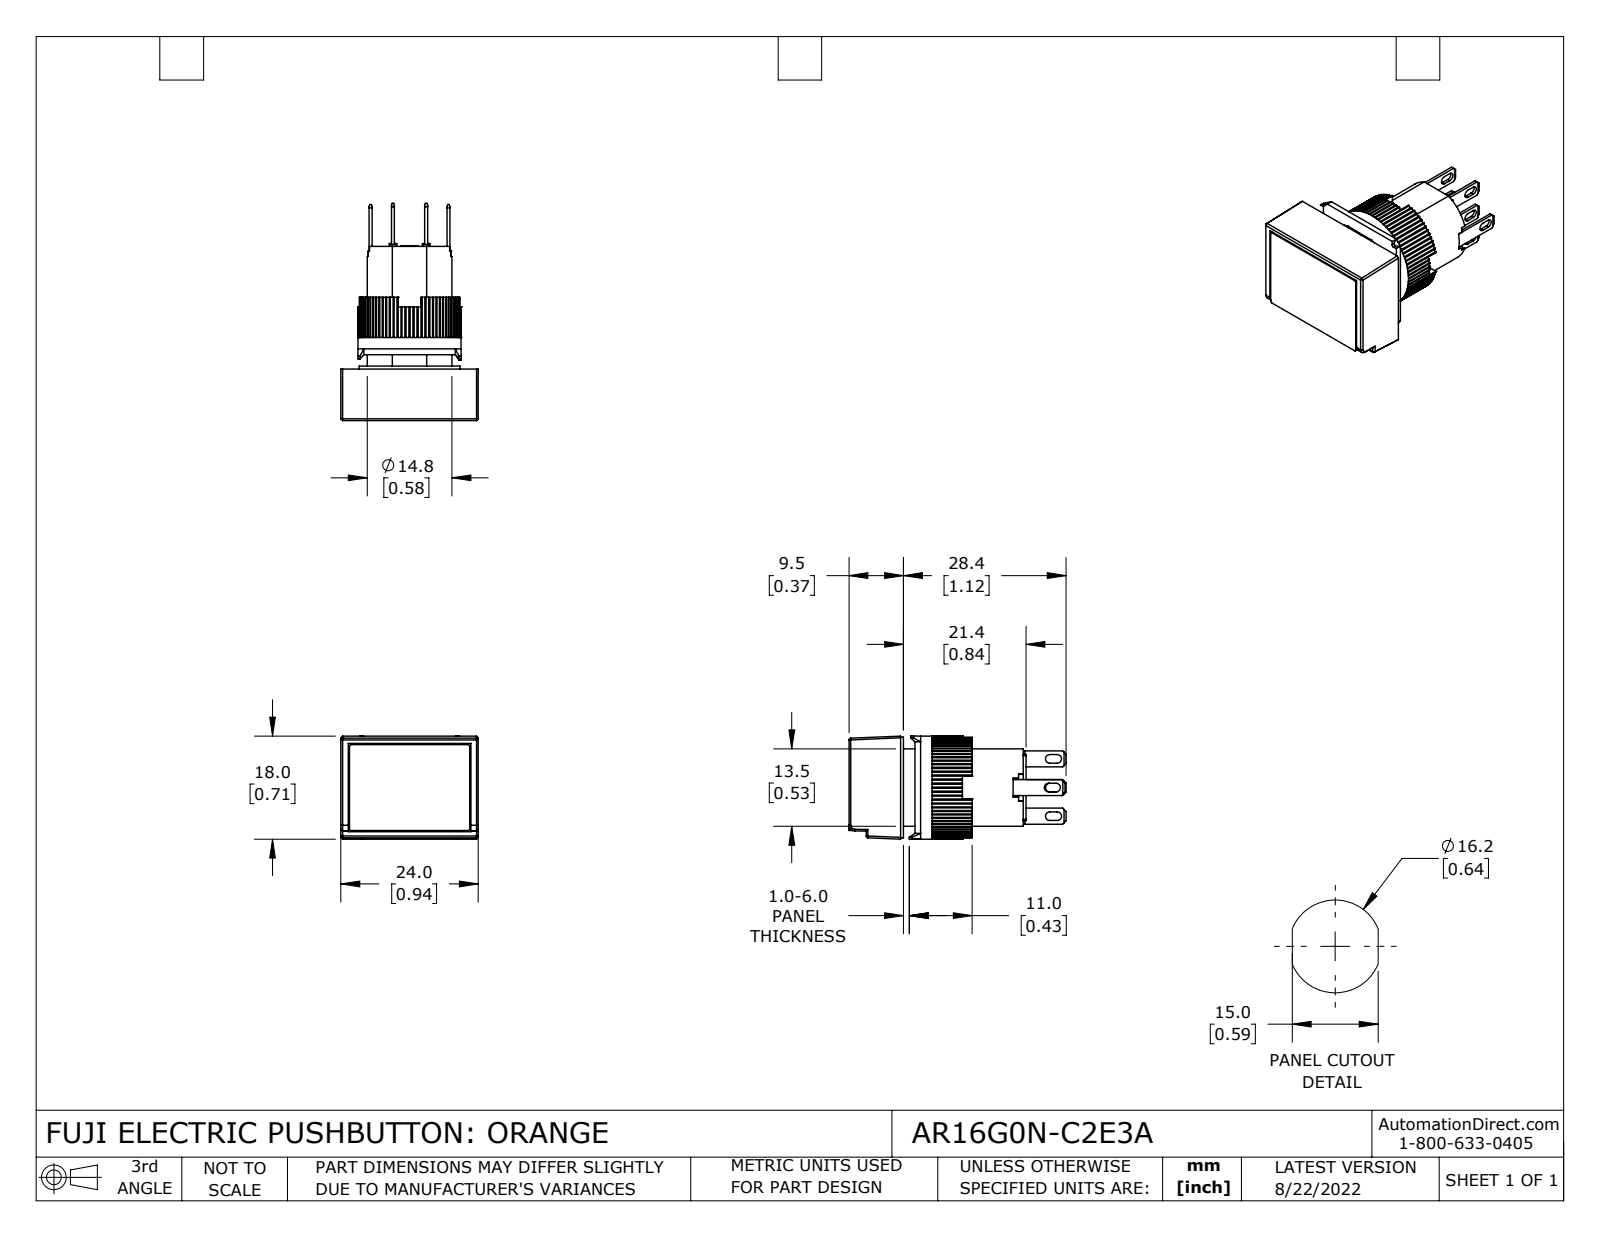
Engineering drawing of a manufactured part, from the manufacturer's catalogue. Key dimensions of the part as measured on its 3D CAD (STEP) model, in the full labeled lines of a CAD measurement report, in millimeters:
Part name (STEP PRODUCT): AR16G0N-C2E3A
STEP written by: SolidWorks 2021 (CONFIG_CONTROL_DESIGN)
Units: millimetres
Bodies: 14 solids, 841 faces (654 planar, 181 cylindrical, 6 other)
Overall size (bounding box): 37.9 × 24 × 18
Volume: 7 340 mm³ · Surface area: 6 131 mm²
Round holes (diameter × count): ⌀13.8 ×1, ⌀14.8 ×1
Round bosses / shafts (diameter × count): ⌀18 ×1, ⌀17.6 ×1
Partial cylindrical surfaces — rounded edges, fillets, slot ends (radius × count): R0.3 ×80, R0.2 ×12, R0.8 ×8, R0.3 ×6, R1 ×1
Main face-to-face distances: 5.4, 9, 3.6, 8.9, 12.5, 3.5, 0.5, 21.4, 1.5, 11.5
